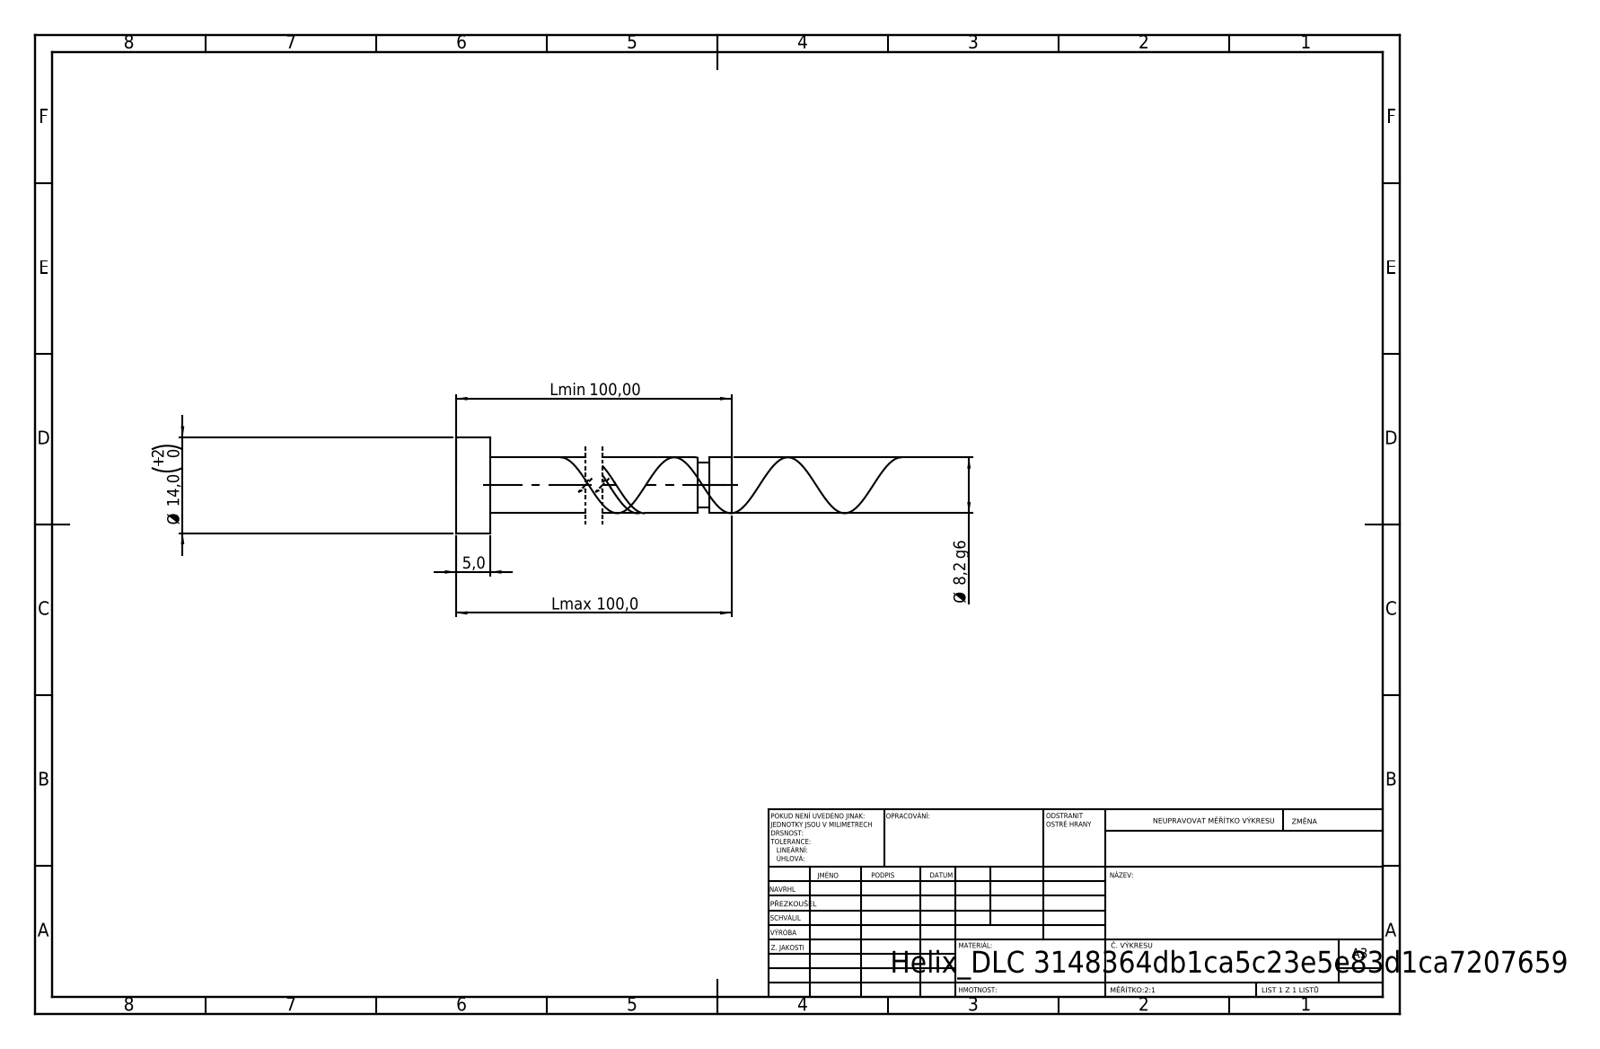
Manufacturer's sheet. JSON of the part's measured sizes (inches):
{"step_written_by": "SolidWorks 2019 (CONFIG_CONTROL_DESIGN)", "units": "inches", "bodies": {"solids": 1, "faces": 21, "planar": 6, "cylindrical": 14, "other": 1}, "overall_size": [3.937, 0.551, 0.551], "volume_in3": 0.348, "surface_area_in2": 4.796, "round_bosses_or_shafts": [[0.551, 1], [0.323, 1], [0.258, 1]], "face_to_face_distances": [0.197, 3.937, 3.74, 3.809, 3.613, 0.128, 3.745, 3.548, 0.065, 0.192]}
